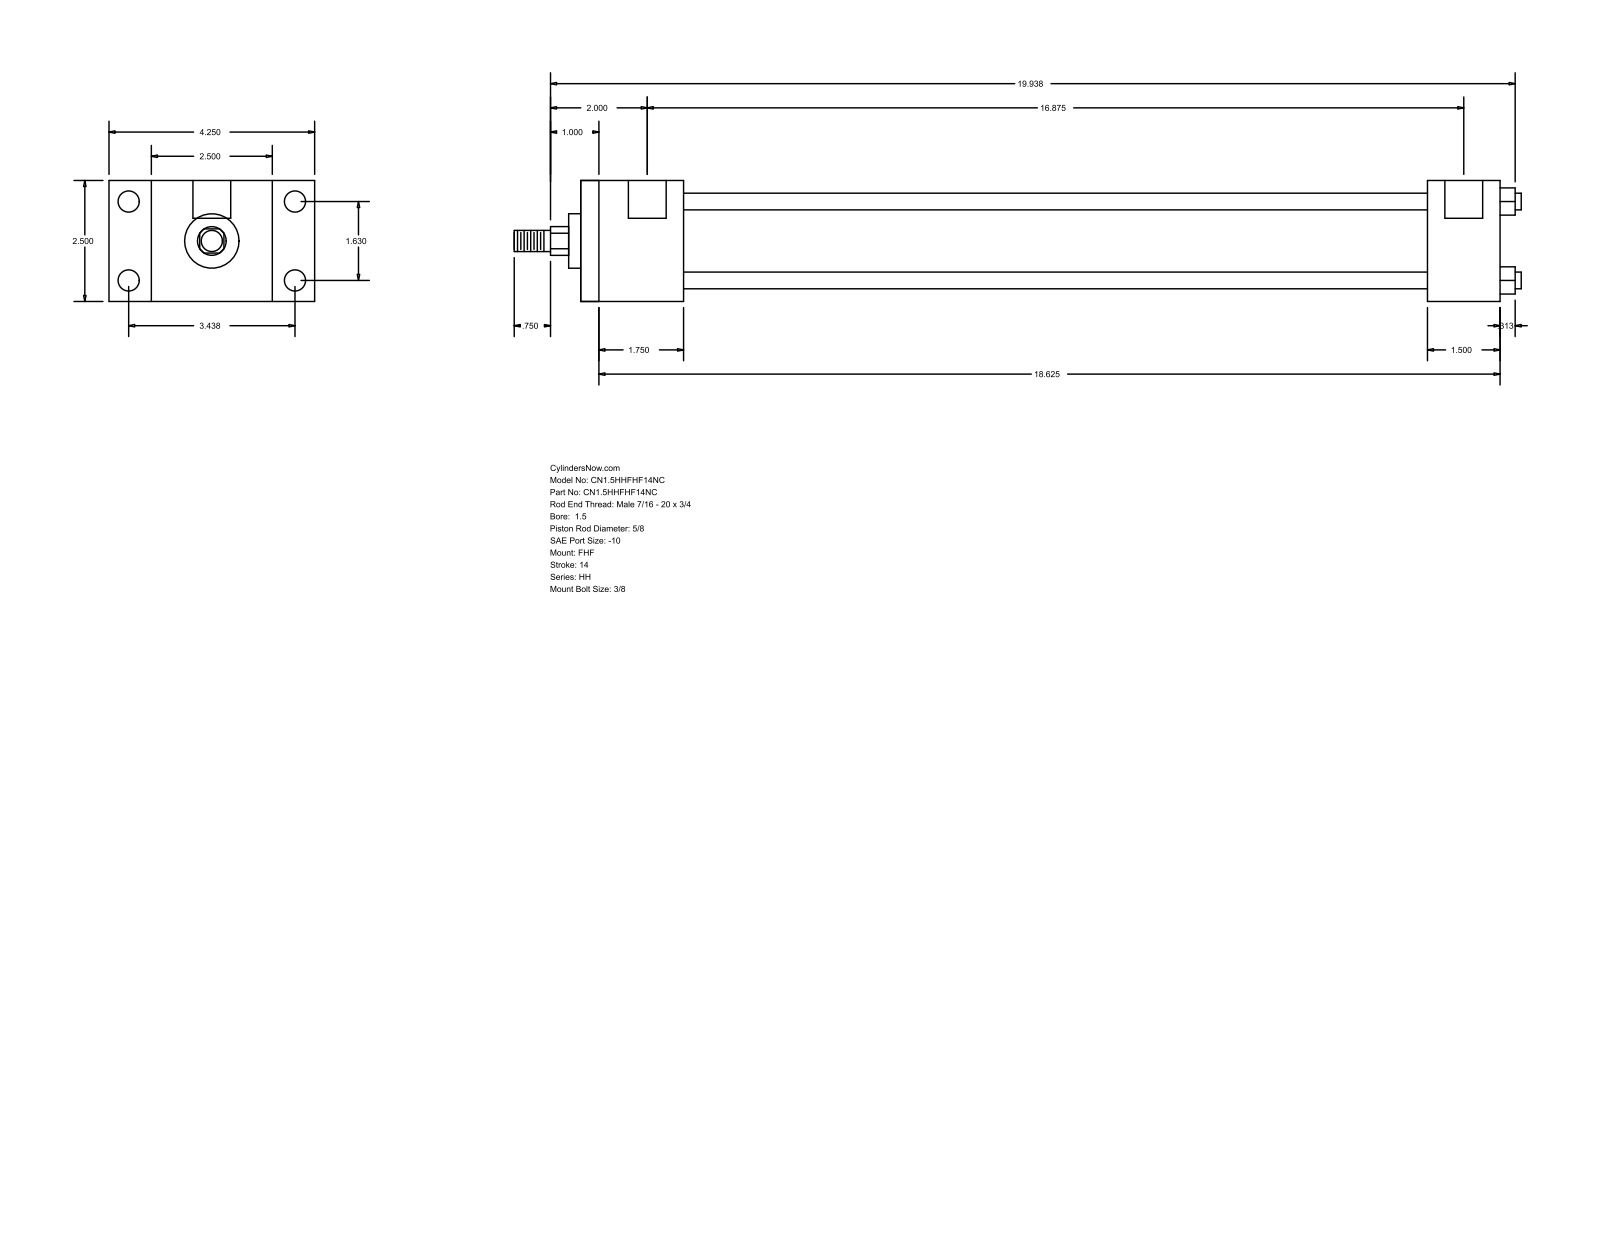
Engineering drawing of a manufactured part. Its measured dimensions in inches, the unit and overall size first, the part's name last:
Units: inches
Overall size (bounding box): 20.813 × 4.25 × 2.5
Round holes (diameter × count): ⌀0.219 ×4, ⌀0.438 ×4, ⌀0.781 ×2
Round bosses / shafts (diameter × count): ⌀0.345 ×4, ⌀1.75 ×1, ⌀1.125 ×1, ⌀0.625 ×1, ⌀0.437 ×1
Partial cylindrical surfaces — rounded edges, fillets, slot ends (radius × count): R0.297 ×1
Main face-to-face distances: 2.5, 0.875, 3.375, 2.125, 4.25, 19, 16.875, 1.5, 17.5, 15.375
Hole centre spacings: 1.63, 3.438, 3.805, 17, 0.062, 0.063, 16.875, 16.937
Bodies: 0 solids, 88 faces (60 planar, 28 cylindrical, 0 other)
Part name (STEP PRODUCT): HH_FHF__0150_0.625
STEP written by: GSSL Pune (CONFIG_CONTROL_DESIGN)
